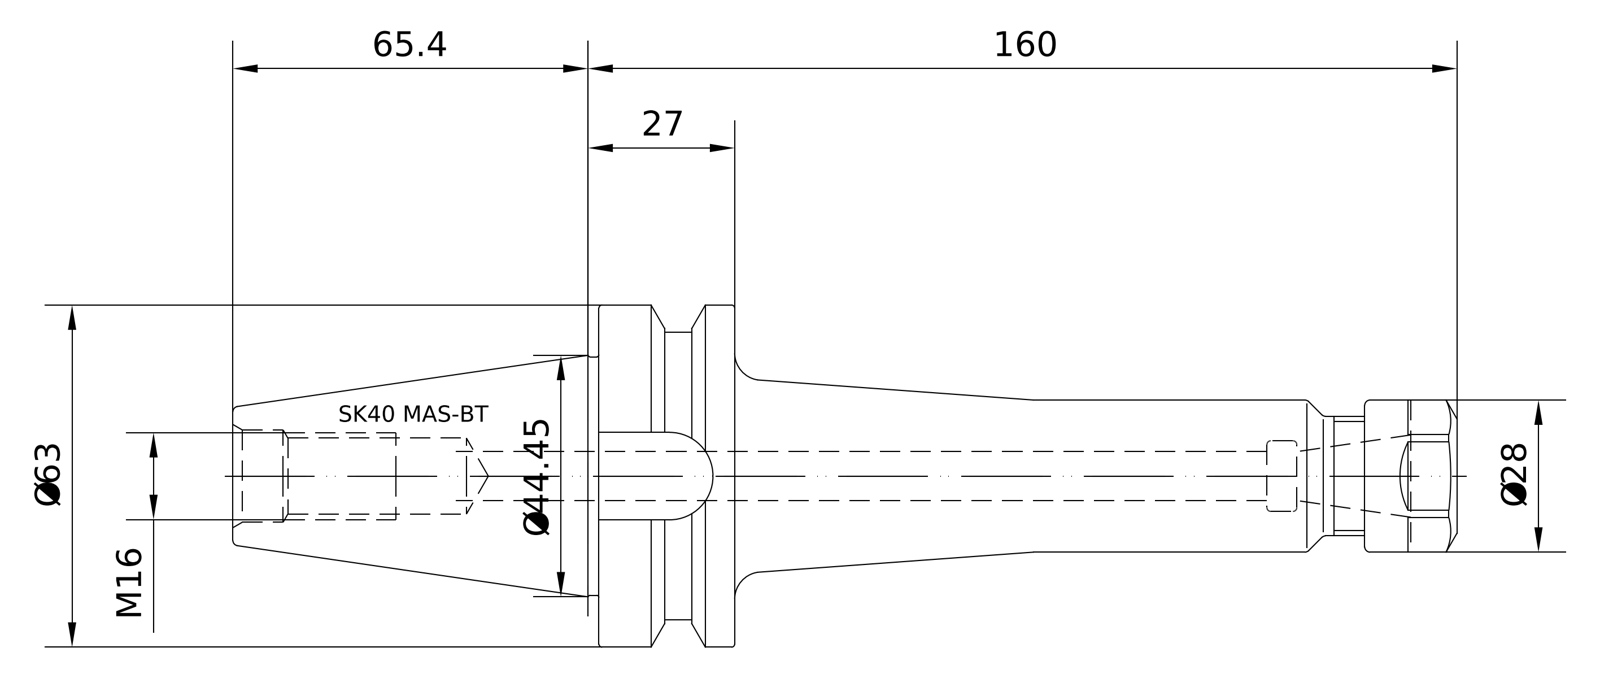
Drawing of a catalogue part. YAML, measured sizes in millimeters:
part_name: "40-522-16; 83-912-16; 40-522-16_ASM"
step_written_by: "PRO/ENGINEER BY PARAMETRIC TECHNOLOGY CORPORATION, 2010430 (CONFIG_CONTROL_DESIGN)"
units: millimeters
bodies: {solids: 2, faces: 130, planar: 34, cylindrical: 26, other: 70}
overall_size: [225.4, 62.98, 62.98]
volume: 212206
surface_area: 35714
round_holes:
  - {diameter: 10.5, count: 1}
  - {diameter: 13.84, count: 1}
  - {diameter: 17.01, count: 1}
  - {diameter: 17.5, count: 1}
round_bosses_or_shafts:
  - {diameter: 62.98, count: 1}
  - {diameter: 52.75, count: 1}
  - {diameter: 43.75, count: 1}
  - {diameter: 28, count: 1}
  - {diameter: 22, count: 1}
  - {diameter: 16.01, count: 1}
partial_cylinders:
  - {radius: 8.1, count: 1}
face_to_face_distances: [25, 140.2, 115.2, 158, 133, 17.8, 44.9, 9.95, 34.95, 92.4]
